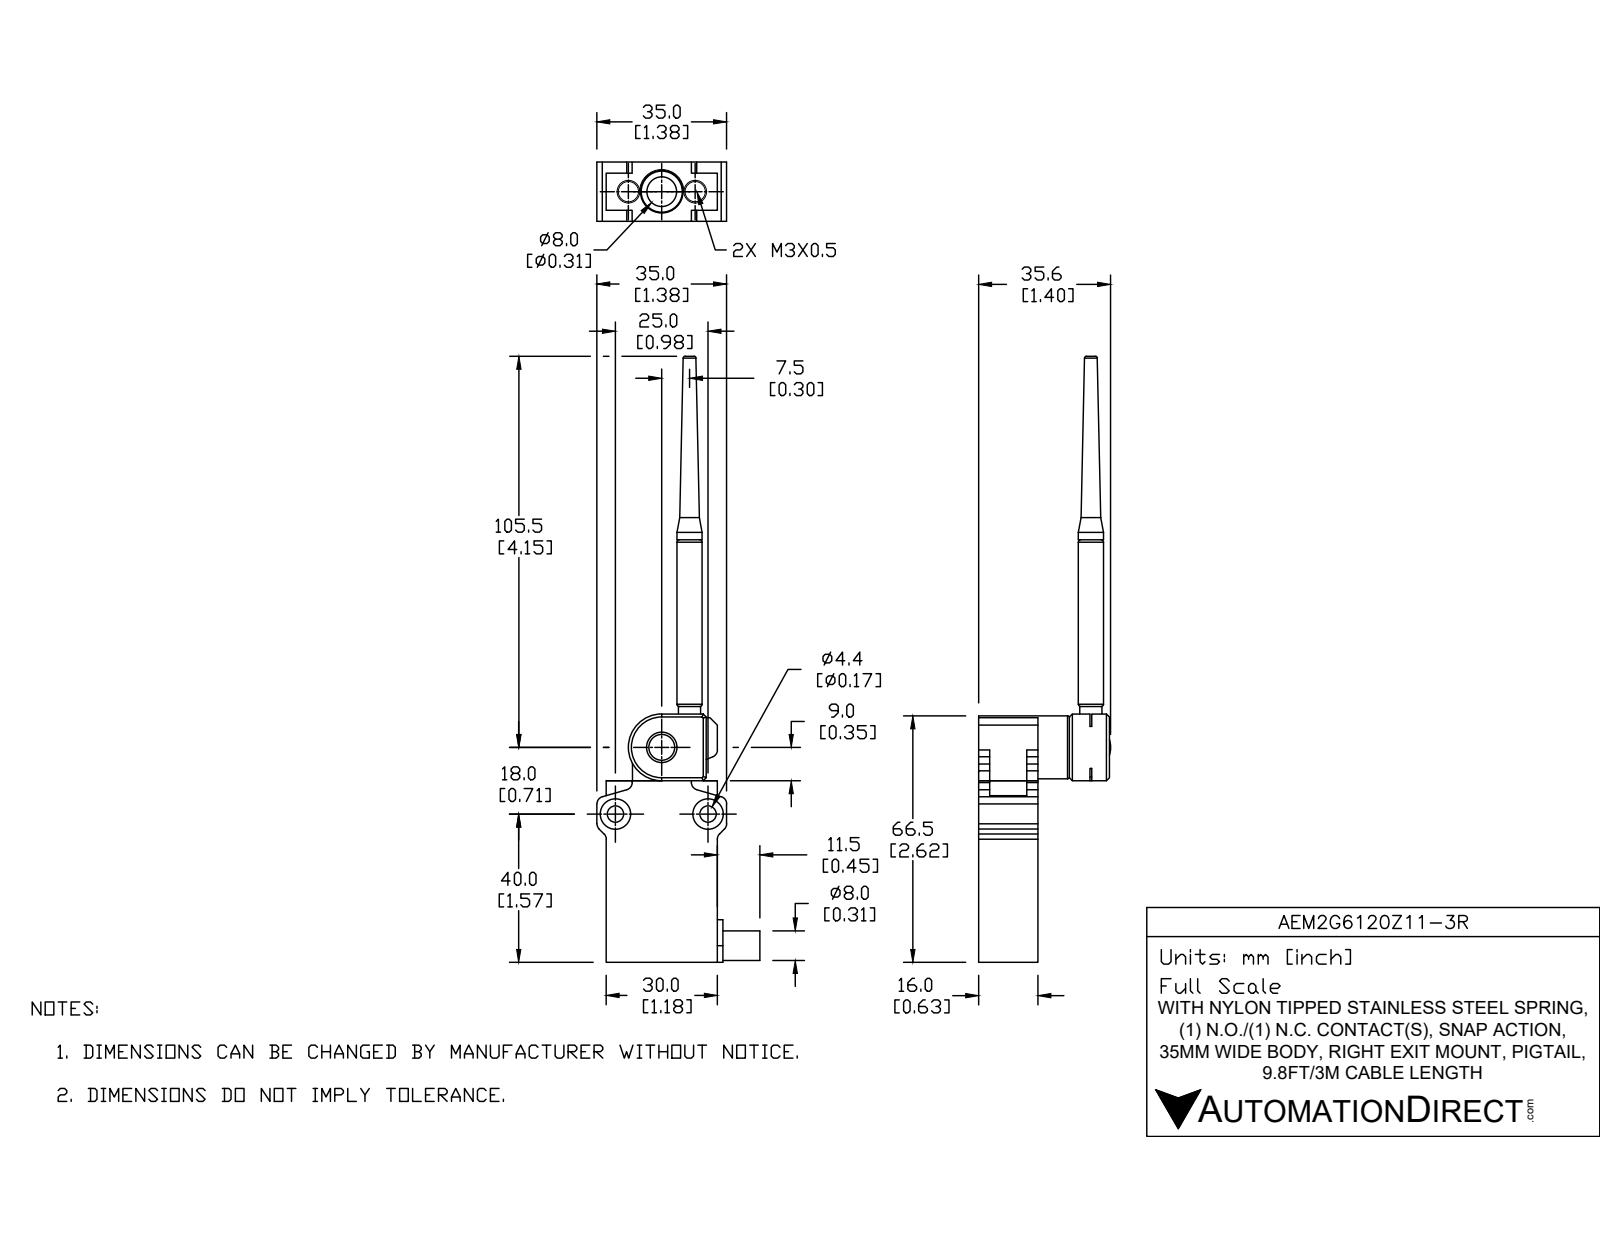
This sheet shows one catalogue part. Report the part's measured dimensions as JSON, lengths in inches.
{"part_name": "AEM2G6120Z11-3R", "step_written_by": "SolidWorks 2017 (AUTOMOTIVE_DESIGN)", "units": "inches", "bodies": {"solids": 9, "faces": 183, "planar": 101, "cylindrical": 59, "other": 23}, "overall_size": [6.358, 1.87, 1.374], "volume_in3": 1.996, "surface_area_in2": 23.45, "round_holes": [[0.118, 2], [0.173, 2], [0.323, 2], [0.138, 1], [0.197, 1], [0.236, 1], [0.315, 1]], "round_bosses_or_shafts": [[0.622, 1], [0.323, 1], [0.276, 1], [0.268, 1]], "partial_cylinders_radius": [[0.079, 8], [0.256, 1], [0.354, 1]], "face_to_face_distances": [0.63, 1.181, 0.177, 1.929, 0.354, 0.535, 1.165, 0.358, 0.28, 0.902], "hole_center_spacings": [0.863, 0.748, 0.857, 0.984, 1.065]}
